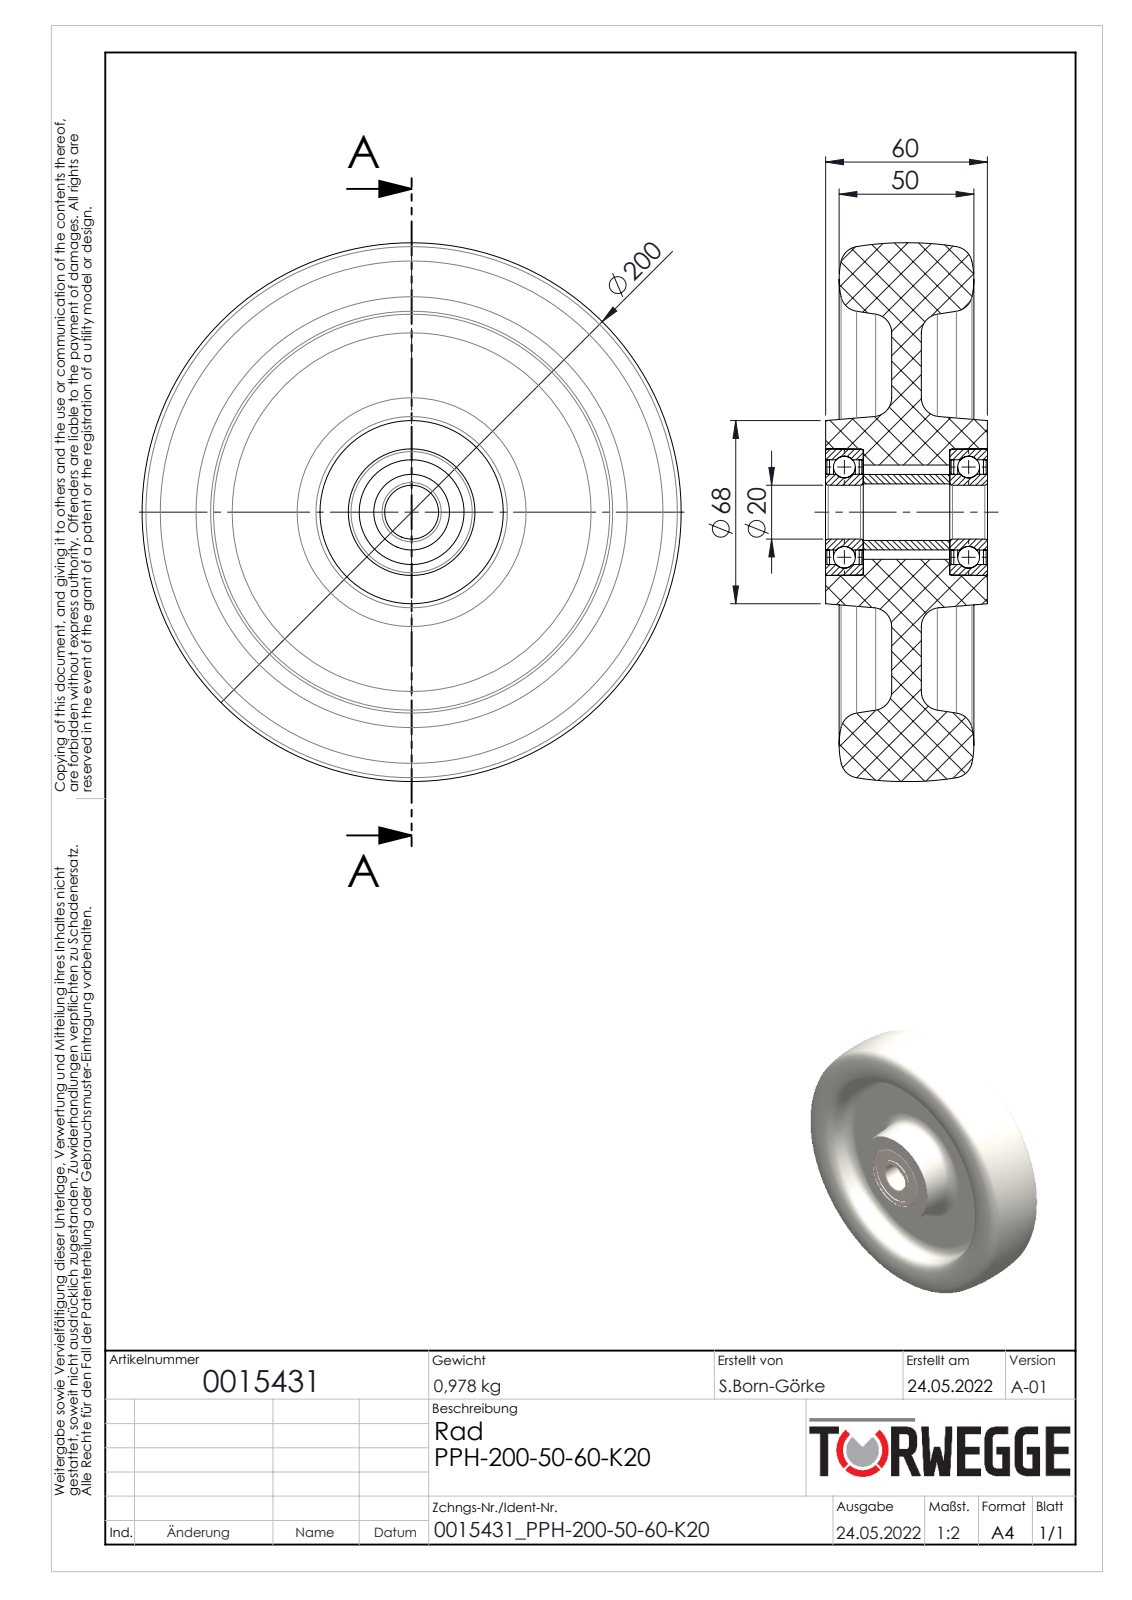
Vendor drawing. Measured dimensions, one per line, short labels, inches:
name: 0015431
written by: SolidWorks 2020 (AUTOMOTIVE_DESIGN)
unit: in
bodies: 12 solids, 142 faces (24 planar, 46 cylindrical, 72 other)
size: 7.875 × 7.874 × 2.366
volume: 61.76 in³; area: 225 in²
holes: 1× ⌀0.787, 1× ⌀0.827, 1× ⌀1.106, 1× ⌀1.378, 1× ⌀1.531
bosses: 1× ⌀1.85, 1× ⌀1.102
face distances: 0.433, 0.965, 1.398, 1.815, 1.813, 0.551, 0.02, 0.059, 0.492, 0.531
